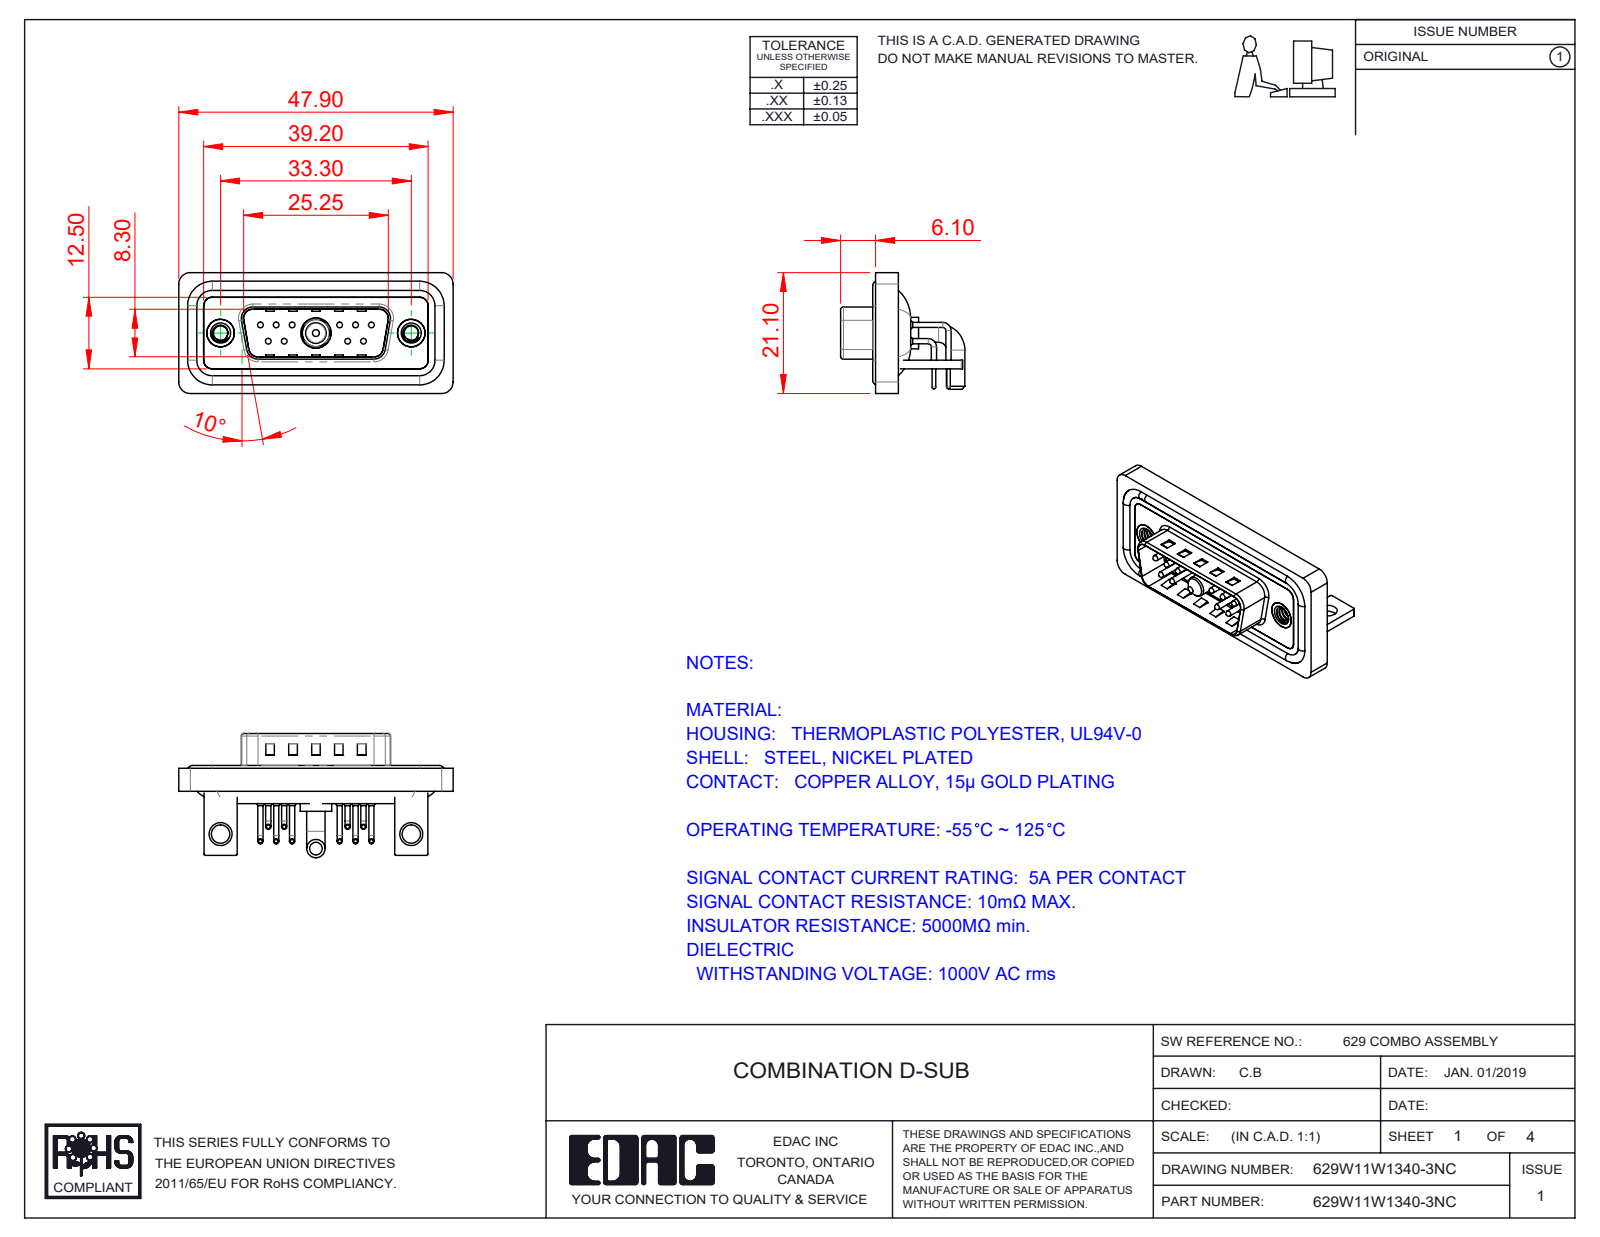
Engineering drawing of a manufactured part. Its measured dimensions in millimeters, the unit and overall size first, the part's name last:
Units: millimetres
Overall size (bounding box): 47.9 × 21.7 × 21.1
Round holes (diameter × count): ⌀0.75 ×10, ⌀1.6 ×10, ⌀2 ×10, ⌀2.5 ×2, ⌀3.2 ×2, ⌀4 ×2, ⌀4.8 ×2, ⌀5 ×2, ⌀4.85 ×1, ⌀5.3 ×1
Round bosses / shafts (diameter × count): ⌀0.9 ×20, ⌀1.5 ×10, ⌀1 ×10, ⌀0.65 ×10, ⌀1.6 ×4, ⌀4.9 ×2, ⌀3.2 ×2, ⌀5.5 ×1
Partial cylindrical surfaces — rounded edges, fillets, slot ends (radius × count): R2 ×21, R1.5 ×18, R0.25 ×16, R1.01 ×10, R0.5 ×9, R1.6 ×8, R1 ×7, R0.6 ×4
Main face-to-face distances: 0.4, 0.8, 1.5, 2.9, 2.1, 1.1, 1.6, 1.2, 3.7, 4.1
Hole centre spacings: 3.16, 2.77, 13.85, 11.08, 16.62, 5.03, 5.04, 5.54
Volume: 5 890 mm³ · Surface area: 9 887 mm²
Bodies: 21 solids, 1641 faces (856 planar, 587 cylindrical, 198 other)
Part name (STEP PRODUCT): Power Pin_30A RA; 629Combo Threaded Rivet_B; 629Combo Waterproof Housing_15 Contacts; 629Combo Stabilizer Bracket (+6 more)
STEP written by: SolidWorks 2023 (CONFIG_CONTROL_DESIGN)
